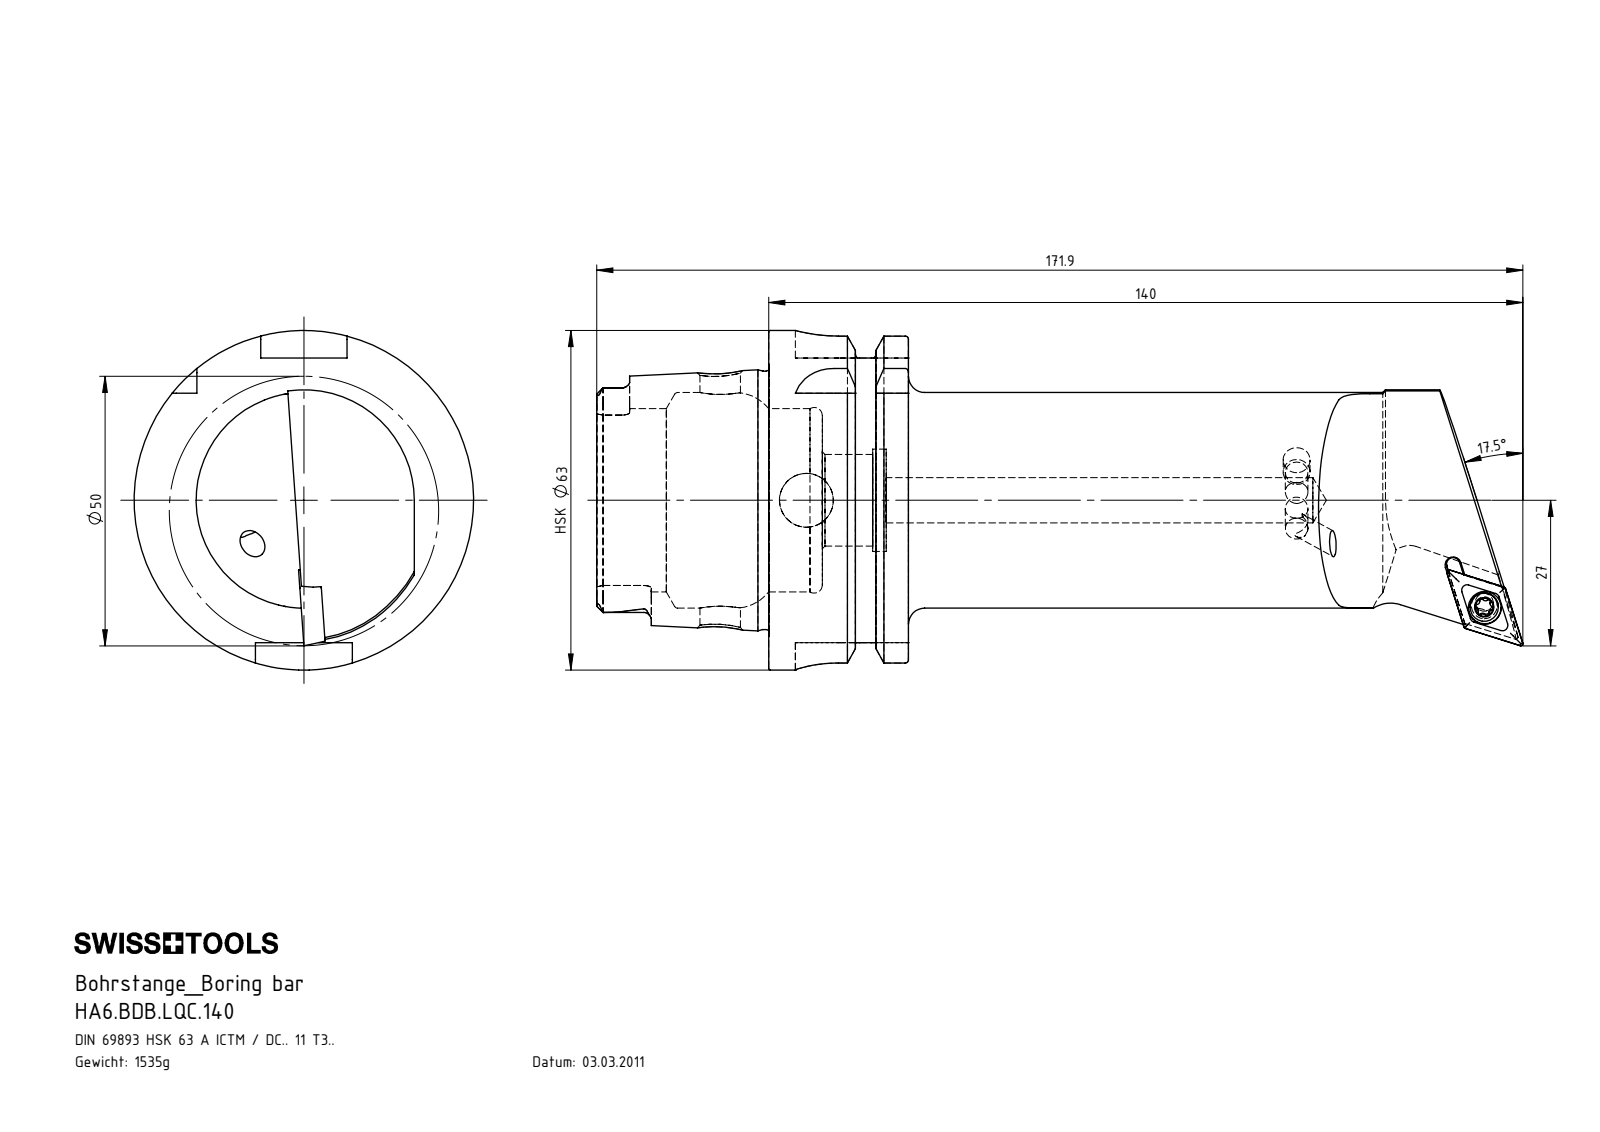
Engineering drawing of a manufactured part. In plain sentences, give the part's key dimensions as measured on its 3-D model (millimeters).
The part is named "HA6-BDB.LQC.140_A; KVT_MB_600_050; WCB-ER2.001.009_A; HA6.BDB.LQC.140 (+1 more)". Its 3-D file was written by "SolidWorks 2017 (AUTOMOTIVE_DESIGN)". It is 5 solids with 311 faces: 79 planar, 91 cylindrical and 141 other. Overall it measures 171.9 by 63 by 63 millimeters. Its volume is 196 931 cubic millimeters and its surface area 38 655 square millimeters. Round holes: 2 of diameter 4.2, 1 of diameter 3.3, 1 of diameter 4, 1 of diameter 4.4, 1 of diameter 5, 1 of diameter 6.1, 1 of diameter 7.5, 1 of diameter 8.4, 1 of diameter 10, 1 of diameter 17, 1 of diameter 19, 1 of diameter 34. Round bosses or shafts: 1 of diameter 63, 1 of diameter 54.95, 1 of diameter 47.94, 1 of diameter 5.25, 1 of diameter 5, 1 of diameter 4. Partial cylindrical surfaces (rounded edges, fillets, slot ends): 6 of radius 0.34, 6 of radius 0.59, 6 of radius 1.4, 4 of radius 8, 2 of radius 2.82, 2 of radius 2.88, 1 of radius 1.25, 1 of radius 3. The main face-to-face distances are 25.95, 16, 9.95, 31.9, 41.85, 57.85, 52.8, 21.8, 11.85, 53.7.
